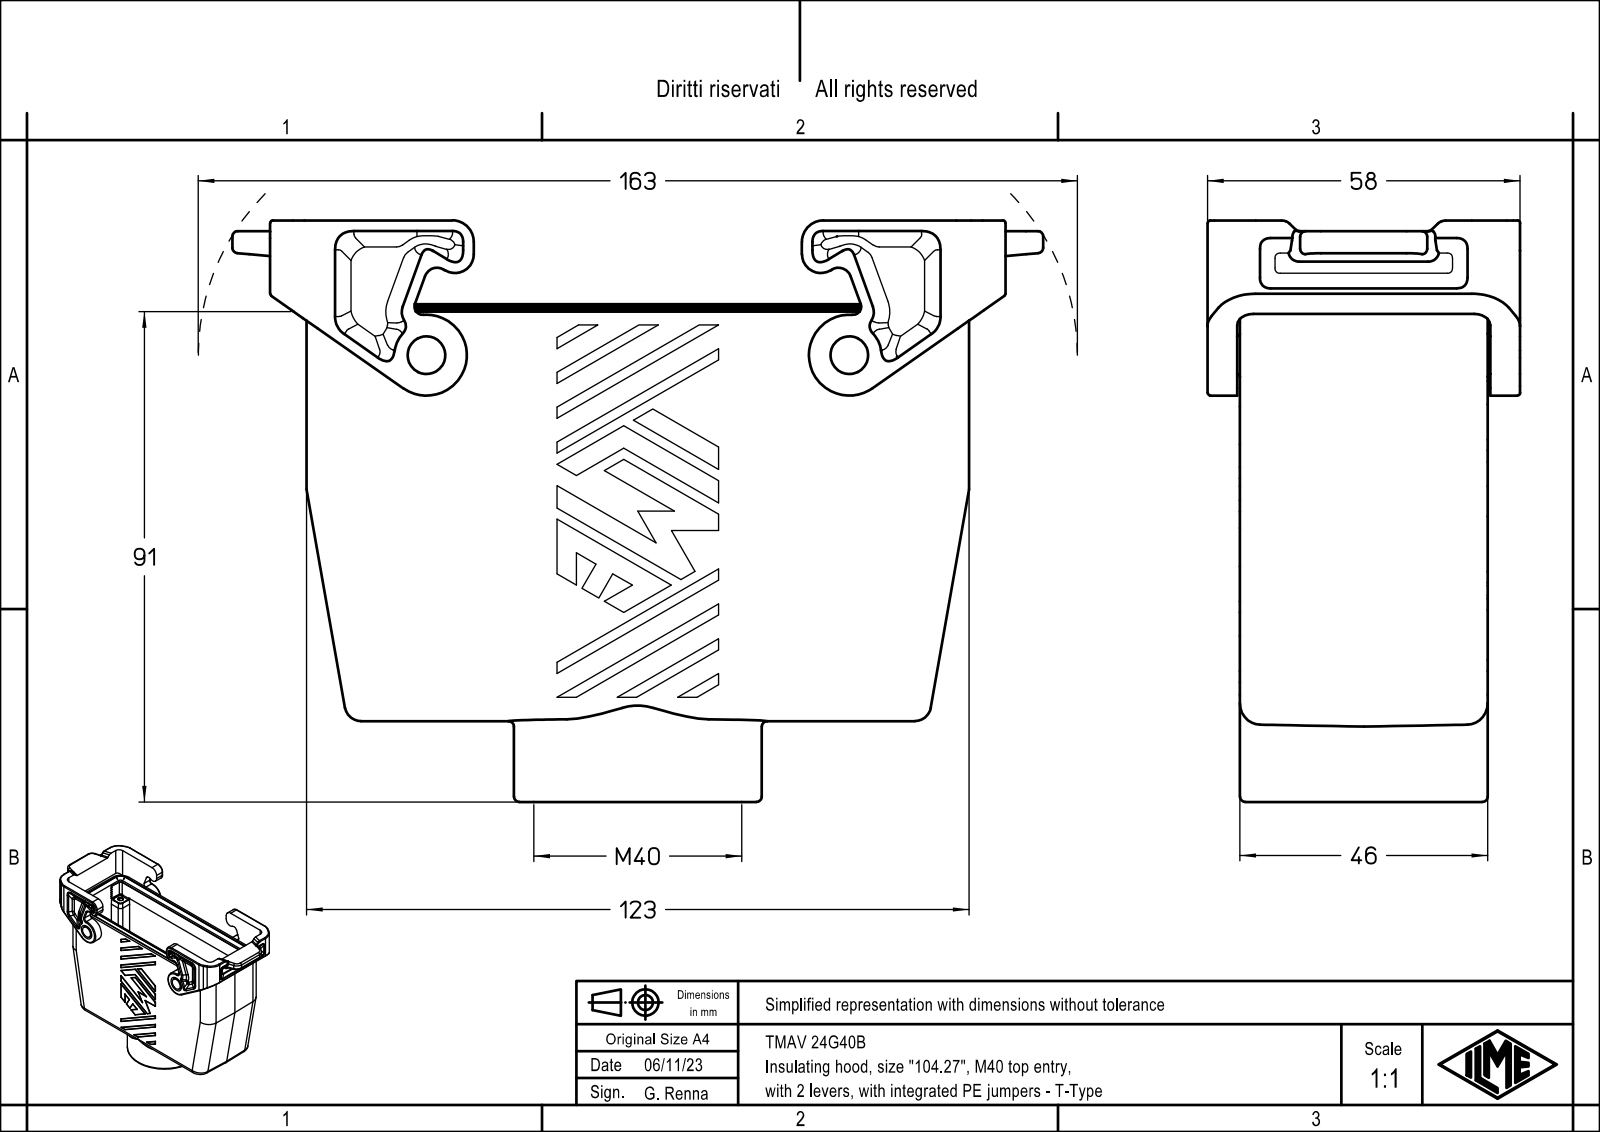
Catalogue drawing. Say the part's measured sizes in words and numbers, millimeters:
The part is named "TMAV 24G40B". Its 3-D file was written by "Creo Elements/Direct Modeling 20.1B 02-Apr-2019 (C) Parametric Technology GmbH (AUTOMOTIVE_DESIGN)". It is 1 solid with 754 faces: 374 planar, 318 cylindrical and 62 other. Overall it measures 150.5 by 107.9 by 58 millimeters. Its volume is 180 382 cubic millimeters and its surface area 75 685 square millimeters. Round holes: 4 of diameter 3.5, 1 of diameter 34, 1 of diameter 38.6. Round bosses or shafts: 2 of diameter 7, 1 of diameter 46. Partial cylindrical surfaces (rounded edges, fillets, slot ends): 88 of radius 0.15, 20 of radius 2, 20 of radius 3, 18 of radius 1.5, 16 of radius 1, 12 of radius 1.3, 8 of radius 6, 8 of radius 7. The main face-to-face distances are 5.4, 40.6, 35.2, 46, 5.9, 0.5, 41.1, 46.5, 34.8, 6.6. The hole center spacings are 53.72, 27, 104, 107.45.
